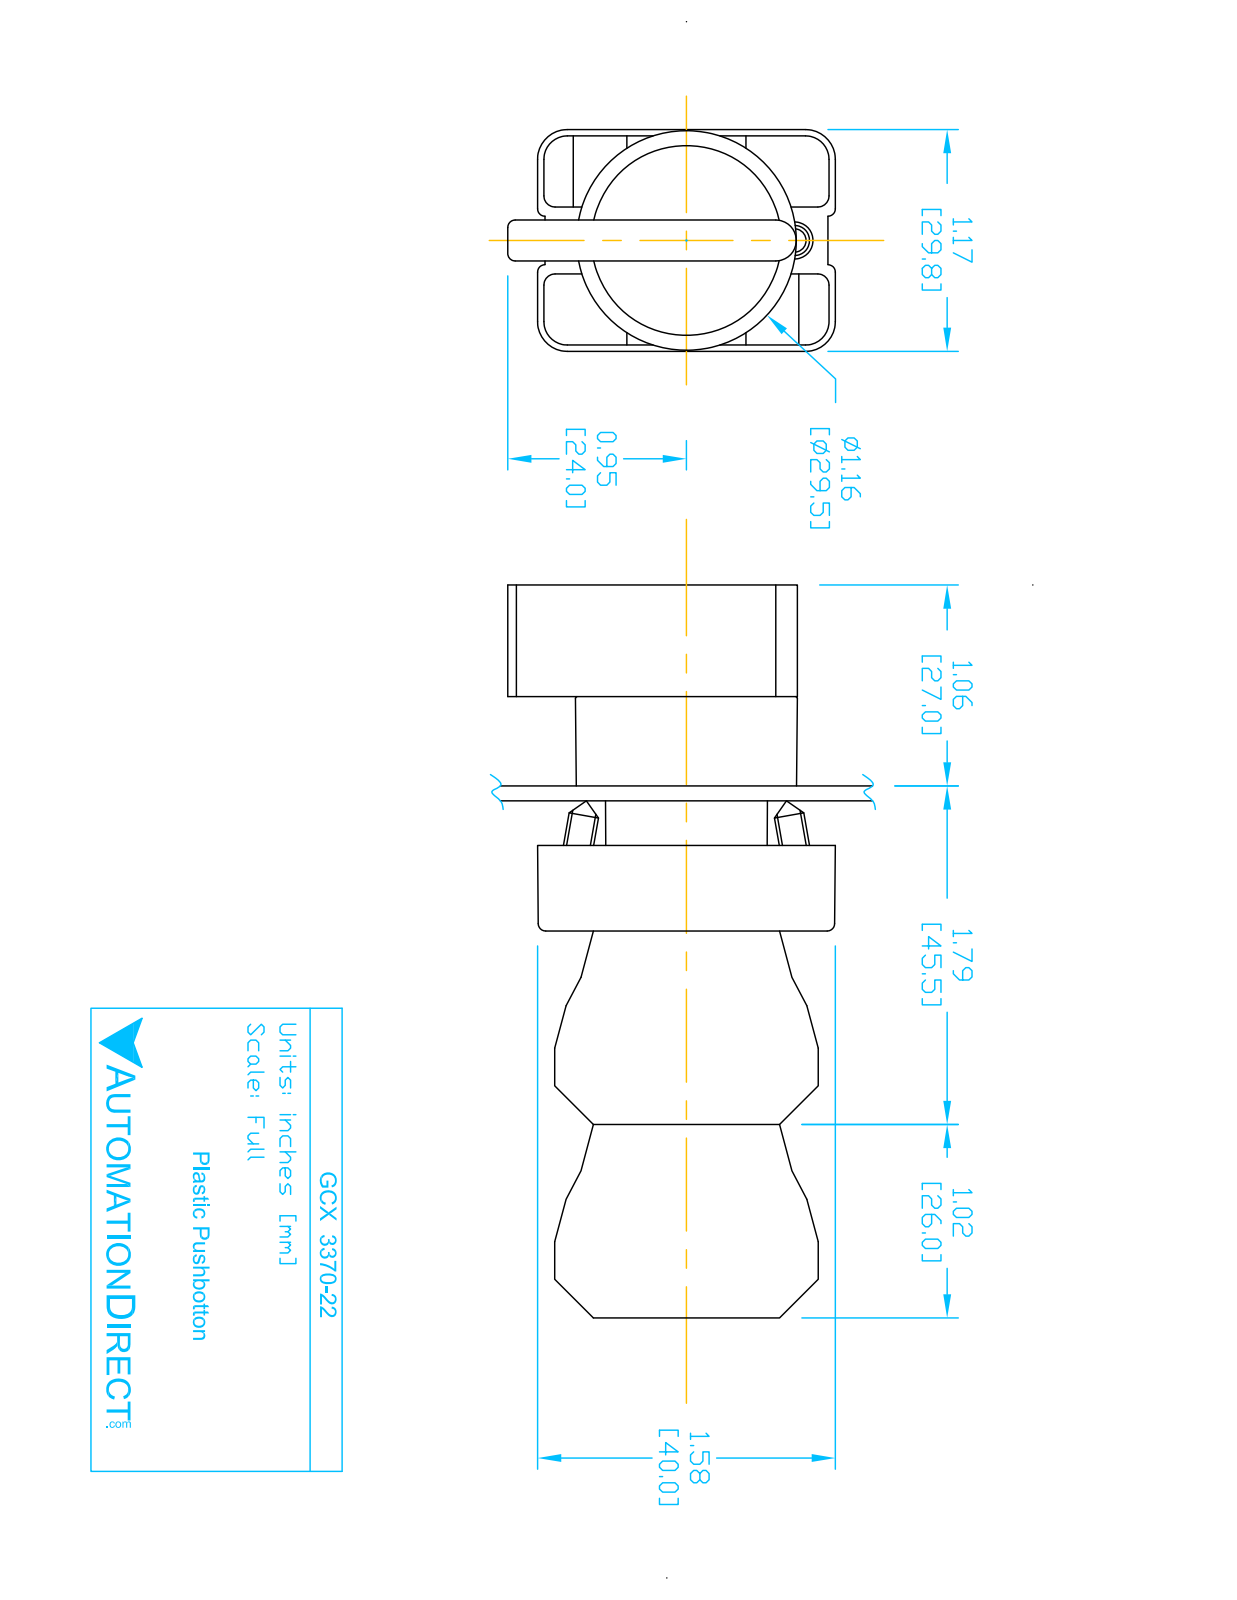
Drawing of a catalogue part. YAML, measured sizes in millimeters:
part_name: "ecx1030; GCX3370-22; ECX3029-2; GCX3370 OPERATOR (+1 more)"
step_written_by: "SolidWorks 2016 (AUTOMOTIVE_DESIGN)"
units: millimeters
bodies: {solids: 9, faces: 675, planar: 457, cylindrical: 179, other: 39}
overall_size: [96.6, 44.5, 29.9]
volume: 63600
surface_area: 31910
round_holes:
  - {diameter: 2, count: 4}
  - {diameter: 2.2, count: 2}
  - {diameter: 3.1, count: 2}
  - {diameter: 3.3, count: 2}
  - {diameter: 5, count: 1}
  - {diameter: 22.3, count: 1}
  - {diameter: 22.6, count: 1}
  - {diameter: 26, count: 1}
round_bosses_or_shafts:
  - {diameter: 4, count: 2}
  - {diameter: 29.8, count: 1}
  - {diameter: 25.5, count: 1}
  - {diameter: 24, count: 1}
  - {diameter: 21.7, count: 1}
  - {diameter: 19.8, count: 1}
partial_cylinders:
  - {radius: 1.5, count: 24}
  - {radius: 1, count: 12}
  - {radius: 3.1, count: 12}
  - {radius: 4, count: 12}
  - {radius: 1, count: 6}
  - {radius: 0.5, count: 2}
  - {radius: 1.6, count: 2}
  - {radius: 2, count: 2}
face_to_face_distances: [15.2, 14.7, 26, 29.9, 0.5, 44.3, 3.1, 18.3, 12, 17.9]
hole_center_spacings: [6, 13.8, 25.6, 24.9, 12, 12.4, 27.6]
